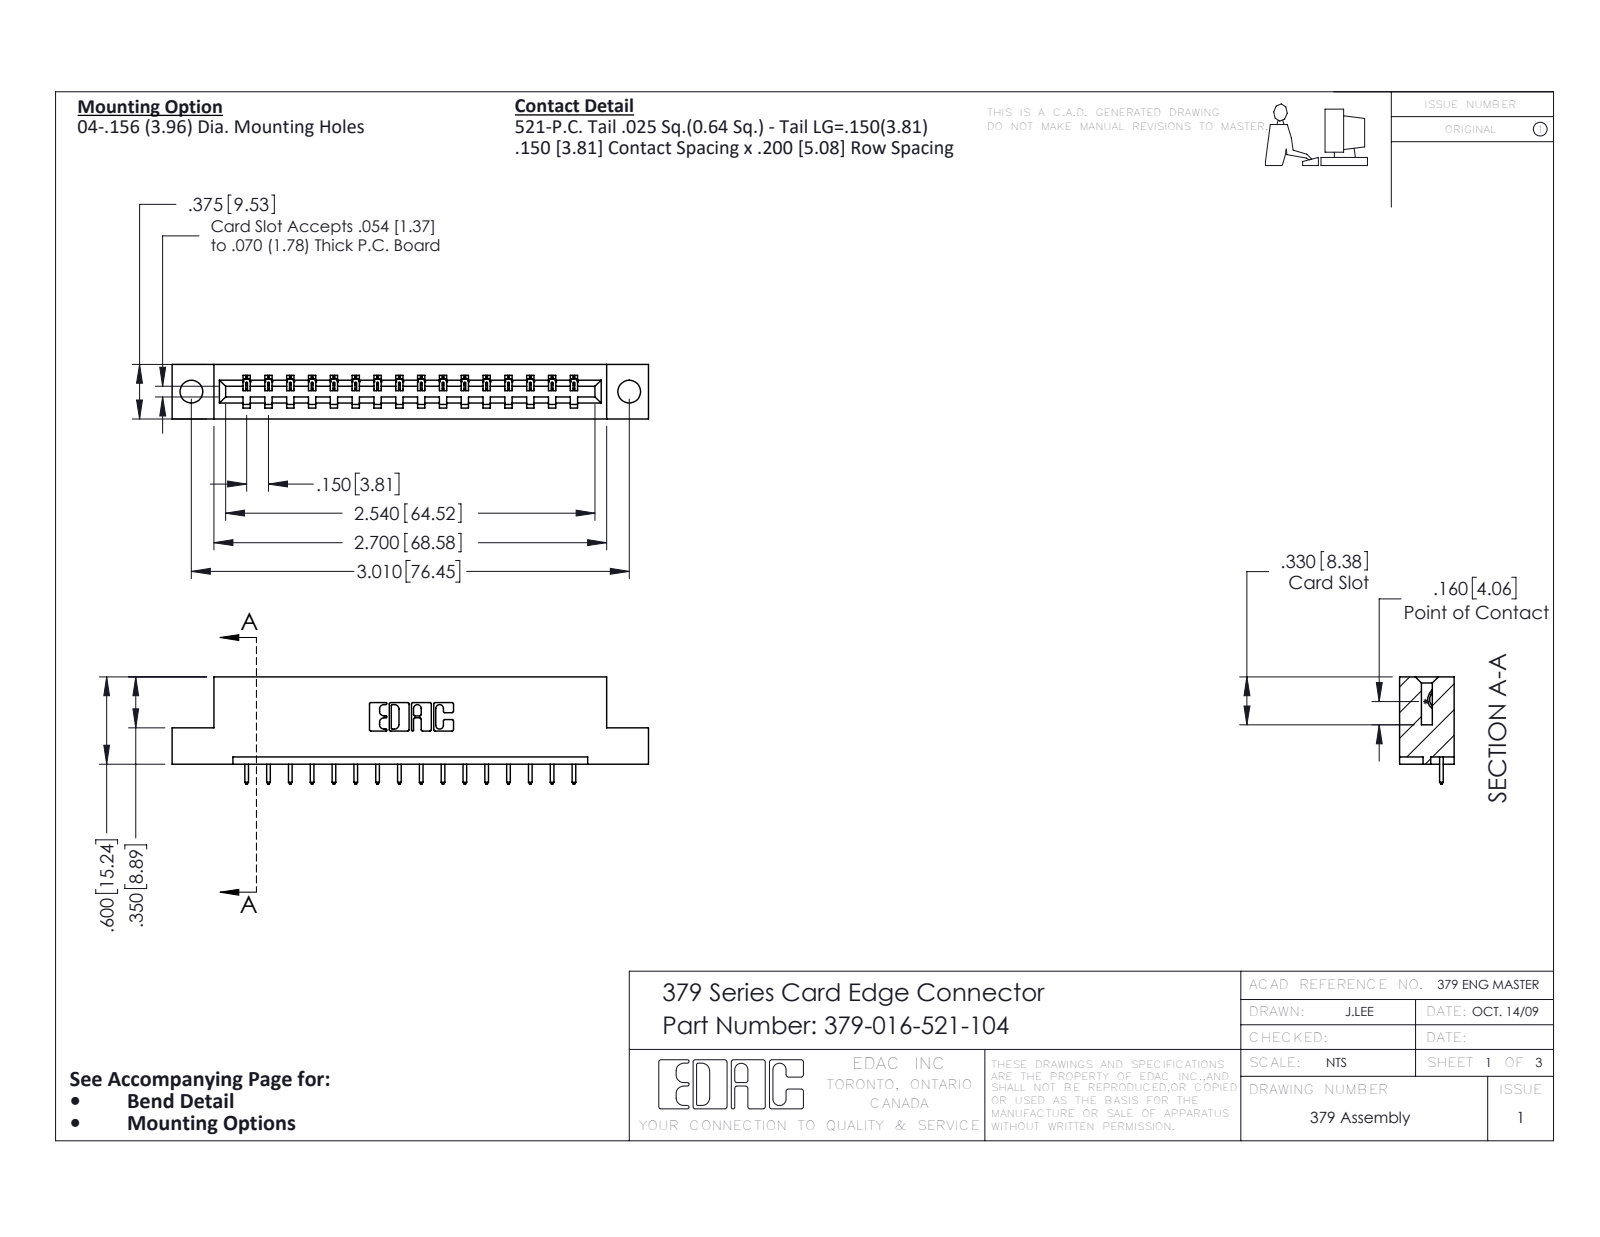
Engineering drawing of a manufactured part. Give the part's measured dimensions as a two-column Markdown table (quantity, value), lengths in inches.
| quantity | value |
| --- | --- |
| part name | 379 Part_Flush - .156 Dia - TH; 345-292-001_345-293-121; 379-016-521-104 |
| STEP written by | SolidWorks 2020 (CONFIG_CONTROL_DESIGN) |
| units | inches |
| bodies | 17 solids, 1042 faces (742 planar, 300 cylindrical, 0 other) |
| overall size | 3.275 × 0.737 × 0.375 |
| volume | 0.506 in³ |
| surface area | 12.34 in² |
| round holes (diameter × count) | 0.156 × 2 |
| partial cylindrical surfaces (radius × count) | 0.006 × 32, 0.01 × 32, 0.01 × 22, 0.007 × 6, 0.031 × 6, 0.026 × 3, 0.014 × 1, 0.022 × 1 |
| main face-to-face distances | 0.3, 0.075, 0.375, 0.6, 0.15, 0.225, 0.45, 0.2, 0.75, 0.9 |
| hole center spacings | 3.01 |
